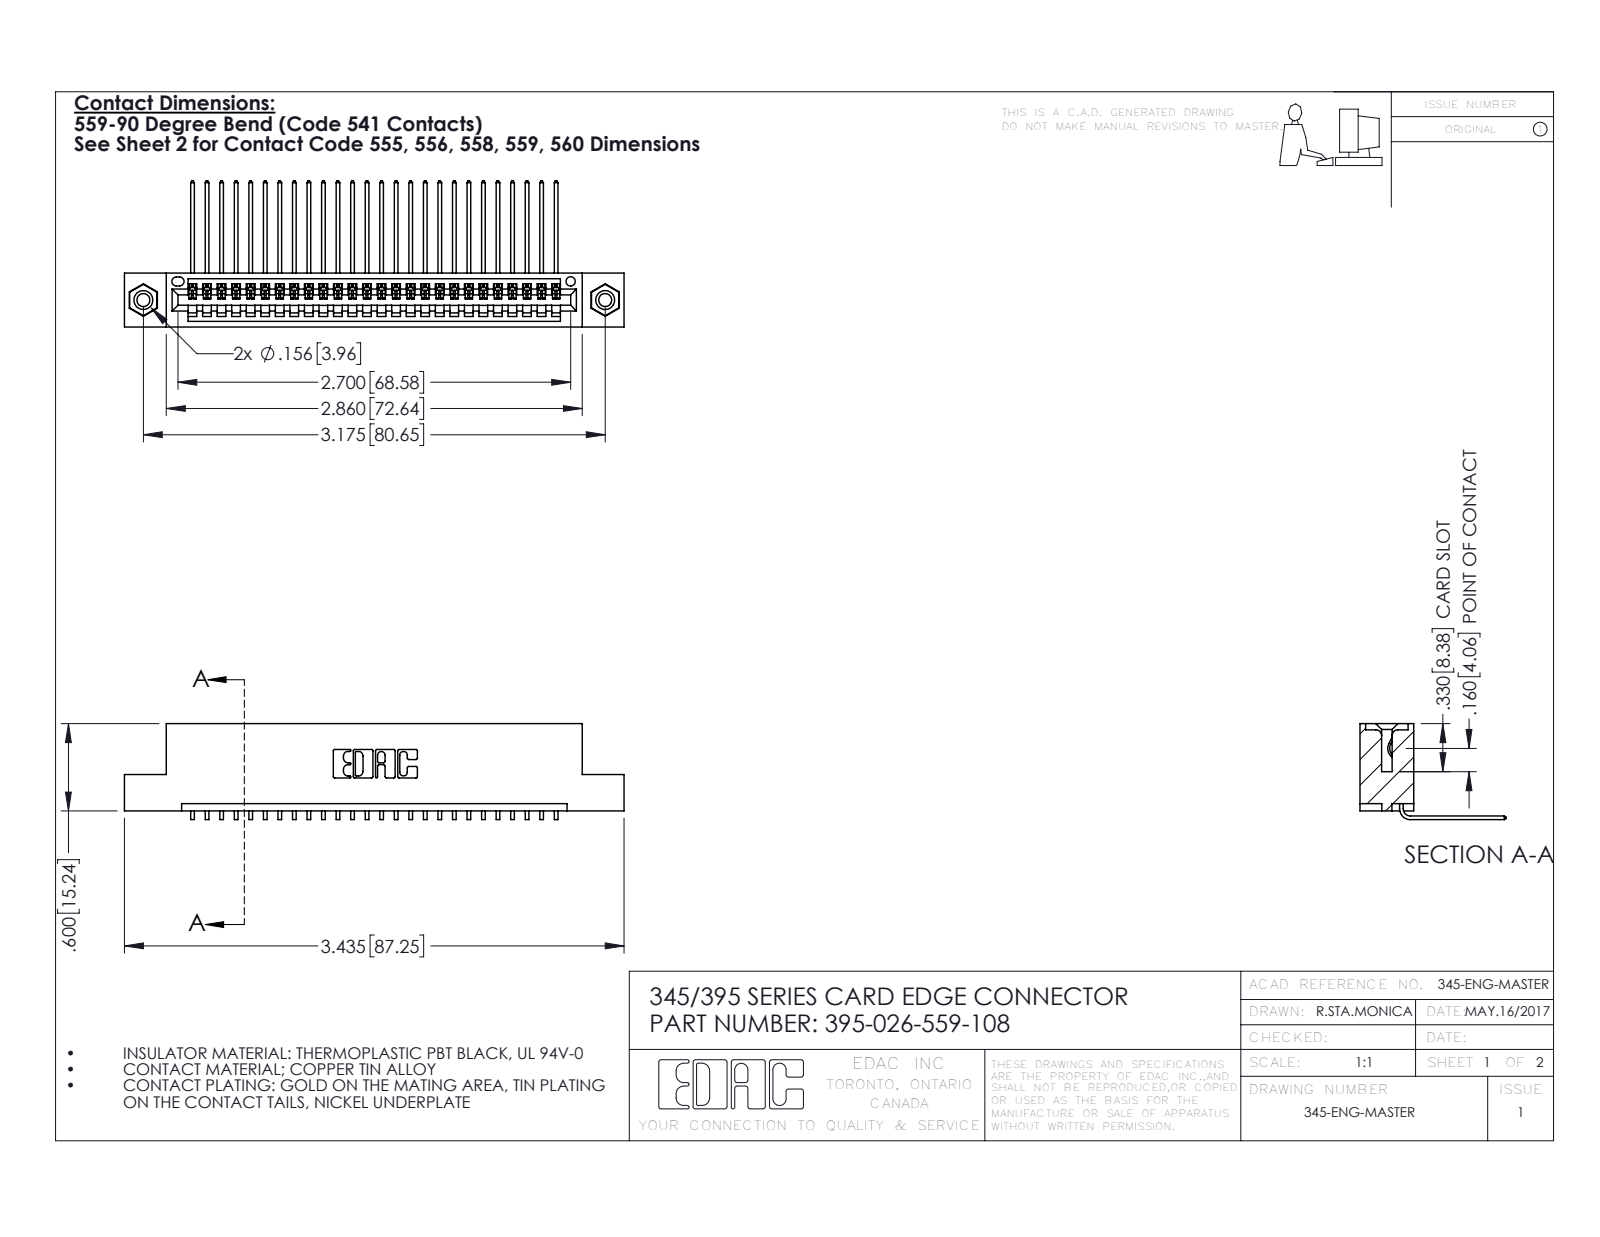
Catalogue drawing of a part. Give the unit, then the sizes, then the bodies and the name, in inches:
Units: inches
Overall size (bounding box): 3.435 × 1.005 × 0.659
Round holes (diameter × count): ⌀0.089 ×2, ⌀0.125 ×2, ⌀0.156 ×2, ⌀0.064 ×1
Round bosses / shafts (diameter × count): ⌀0.155 ×2
Partial cylindrical surfaces — rounded edges, fillets, slot ends (radius × count): R0.006 ×52, R0.01 ×22, R0.007 ×6, R0.031 ×6, R0.026 ×3, R0.031 ×2, R0.04 ×2, R0.014 ×1
Main face-to-face distances: 0.072, 0.298, 0.2, 0.37, 0.098, 0.272, 0.025, 0.225, 0.149, 0.072
Hole centre spacings: 0.27, 2.94, 3.175
Volume: 0.503 in³ · Surface area: 17.45 in²
Bodies: 29 solids, 1746 faces (1204 planar, 526 cylindrical, 16 other)
Part name (STEP PRODUCT): 345-250-001_345-250-003-102; 345-292-001_558 559 Tail - 1; 345 Part_Flush Mounting Lugs - 0.156 Dia-TI; 395-026-559-108
STEP written by: SolidWorks 2016 (CONFIG_CONTROL_DESIGN)
